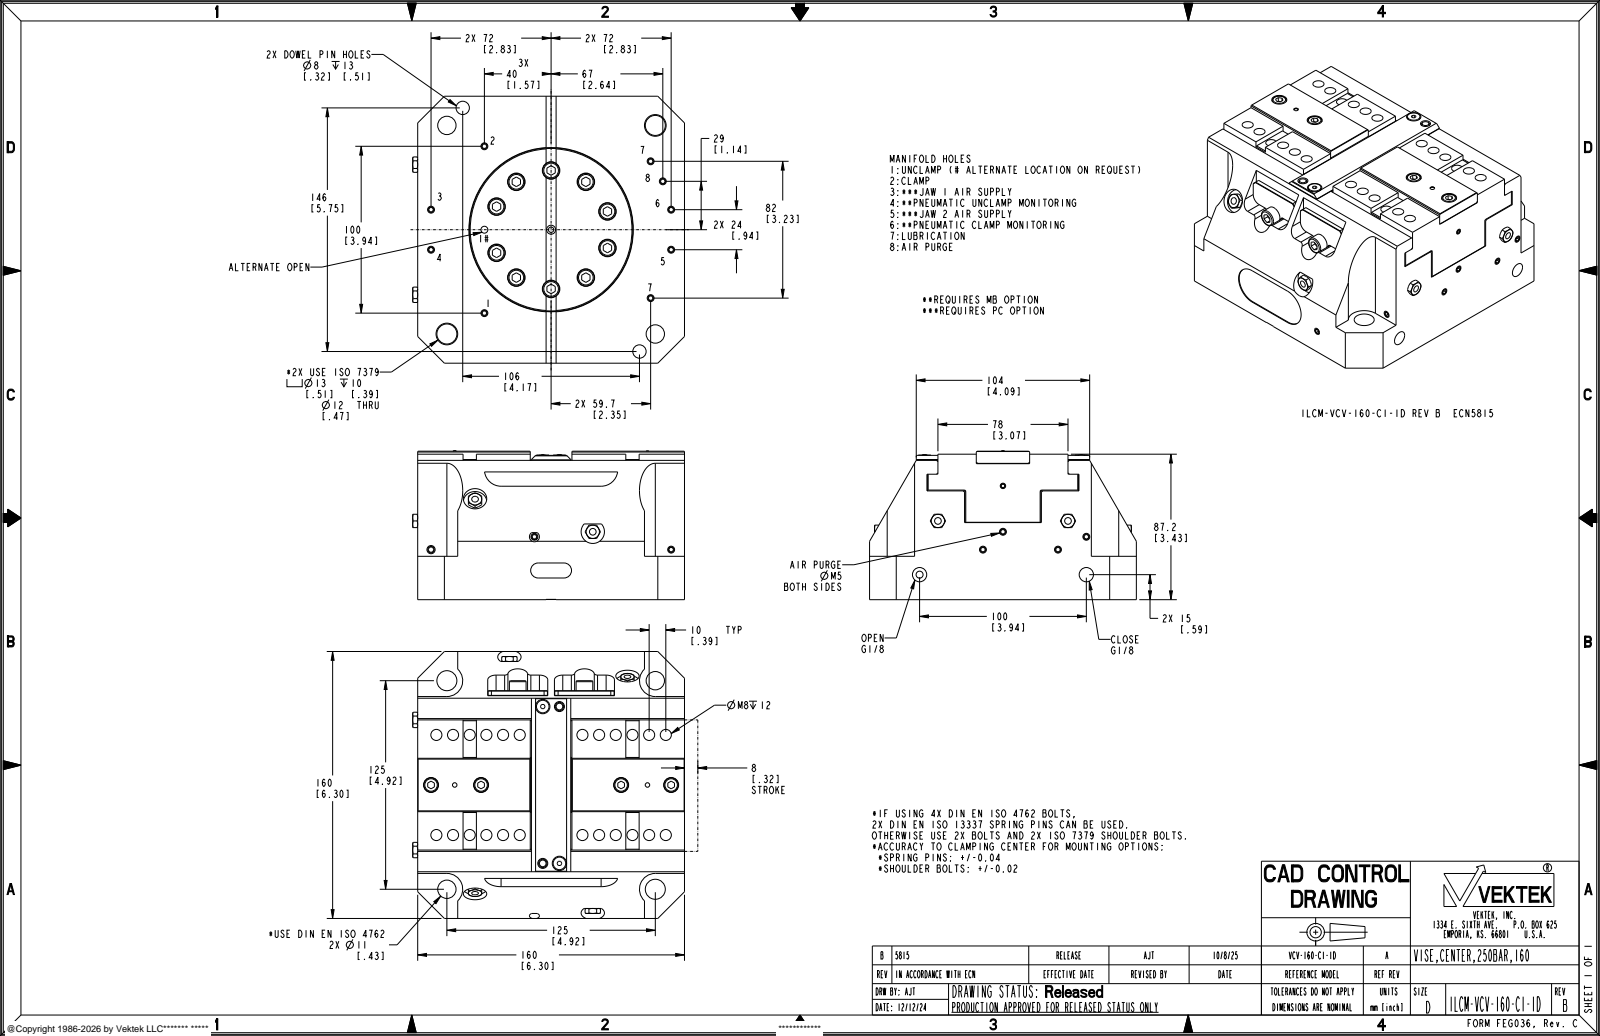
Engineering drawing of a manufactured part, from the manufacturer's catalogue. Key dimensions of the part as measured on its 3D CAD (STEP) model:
Part name (STEP PRODUCT): ISO_4762__-_M4_X_25_1; INGRASSATORE_M6X1_-_COD_D2-31-0; D10910_DIM_A_1; SFERA__X_F83_00_1 (+8 more)
STEP written by: CREO PARAMETRIC BY PTC INC, 2021164 (AUTOMOTIVE_DESIGN)
Units: millimetres
Bodies: 72 solids, 2054 faces (879 planar, 491 cylindrical, 684 other)
Overall size (bounding box): 163 × 160 × 89.41
Volume: 1 776 000 mm³ · Surface area: 243 383 mm²
Round holes (diameter × count): ⌀4.13 ×24, ⌀6.65 ×24, ⌀4.92 ×18, ⌀6.5 ×10, ⌀10.5 ×10, ⌀8 ×6, ⌀3.24 ×4, ⌀5.5 ×4, ⌀9 ×4, ⌀6 ×3, ⌀14 ×3, ⌀2 ×2
Round bosses / shafts (diameter × count): ⌀5 ×24, ⌀6 ×16, ⌀10 ×12, ⌀4 ×7, ⌀6.3 ×6, ⌀8.5 ×4, ⌀7.53 ×2, ⌀7 ×2
Partial cylindrical surfaces — rounded edges, fillets, slot ends (radius × count): R0.4 ×8, R2 ×8, R5 ×8, R2.6 ×4, R3.6 ×4, R9.5 ×4, R12 ×4, R4.5 ×2
Main face-to-face distances: 9.3, 65.2, 55.9, 160, 37.1, 41, 81.5, 72.2, 16.3, 2
Hole centre spacings: 35.5, 57.43, 12.54, 47.27, 51.39, 59.55, 68.08, 69.26
